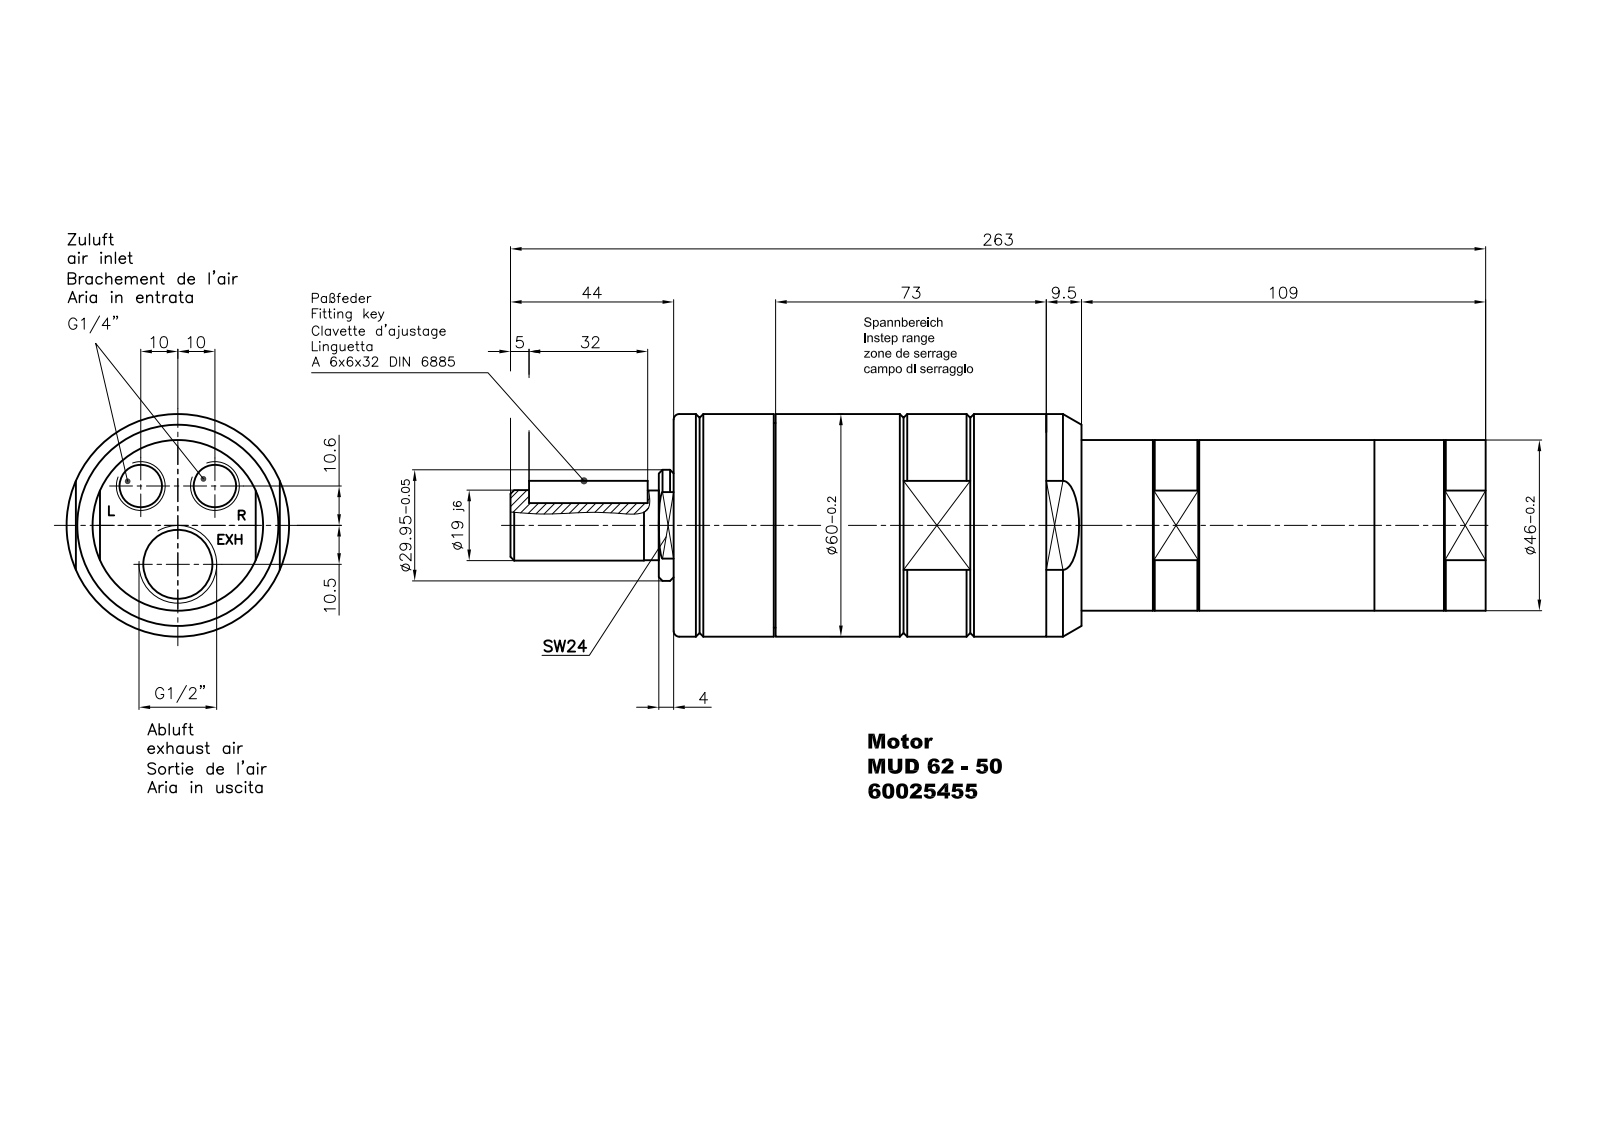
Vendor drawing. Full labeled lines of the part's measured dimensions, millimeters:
Part name (STEP PRODUCT): MUD 62-263
STEP written by: Autodesk Inventor 2012 (AUTOMOTIVE_DESIGN)
Units: millimetres
Bodies: 1 solid, 179 faces (104 planar, 35 cylindrical, 40 other)
Overall size (bounding box): 263 × 60 × 60
Volume: 493 465 mm³ · Surface area: 52 258 mm²
Round holes (diameter × count): ⌀11.45 ×2, ⌀1.55 ×1, ⌀1.6 ×1, ⌀5.5 ×1, ⌀18.63 ×1, ⌀20 ×1, ⌀35 ×1, ⌀46.5 ×1
Round bosses / shafts (diameter × count): ⌀60 ×1, ⌀55.16 ×1, ⌀46 ×1, ⌀29.95 ×1, ⌀19 ×1, ⌀18.8 ×1, ⌀5 ×1
Partial cylindrical surfaces — rounded edges, fillets, slot ends (radius × count): R3 ×2
Main face-to-face distances: 100.5, 219, 118.5, 6.5, 109, 55, 104.5, 110, 9.5, 30
Hole centre spacings: 14.57, 23.35, 10.5, 20
